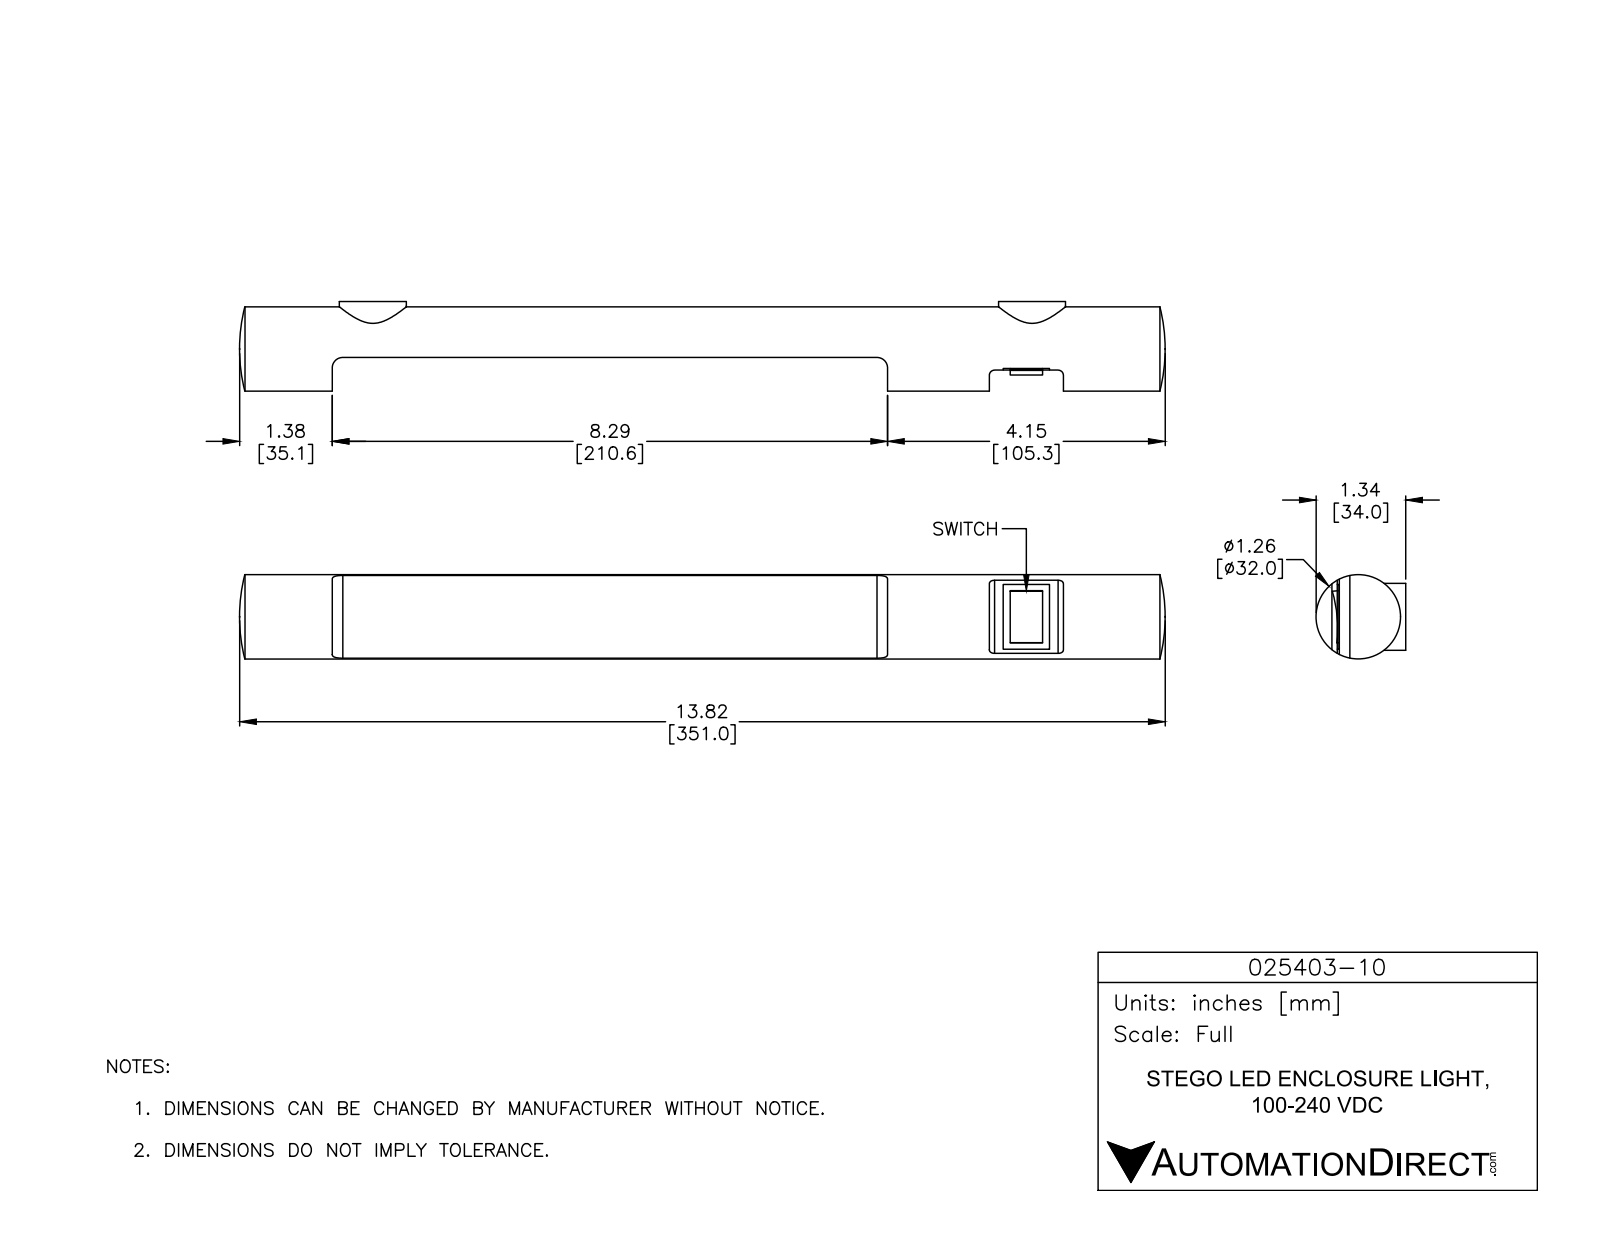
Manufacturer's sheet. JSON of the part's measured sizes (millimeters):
{"part_name": "PRODUCT_NAME_1", "step_written_by": "ACIS (CONFIG_CONTROL_DESIGN)", "units": "millimeters", "bodies": {"solids": 1, "faces": 33, "planar": 17, "cylindrical": 12, "other": 4}, "overall_size": [351, 34, 32], "volume_mm3": 216673, "surface_area_mm2": 35319, "round_bosses_or_shafts": [[25.4, 2], [32, 1]], "partial_cylinders_radius": [[2, 2], [4, 2], [49.14, 1]], "face_to_face_distances": [21.2, 26, 4.8, 25.36, 4.16, 0.64, 210.6, 277.29, 66.69, 249.21]}
